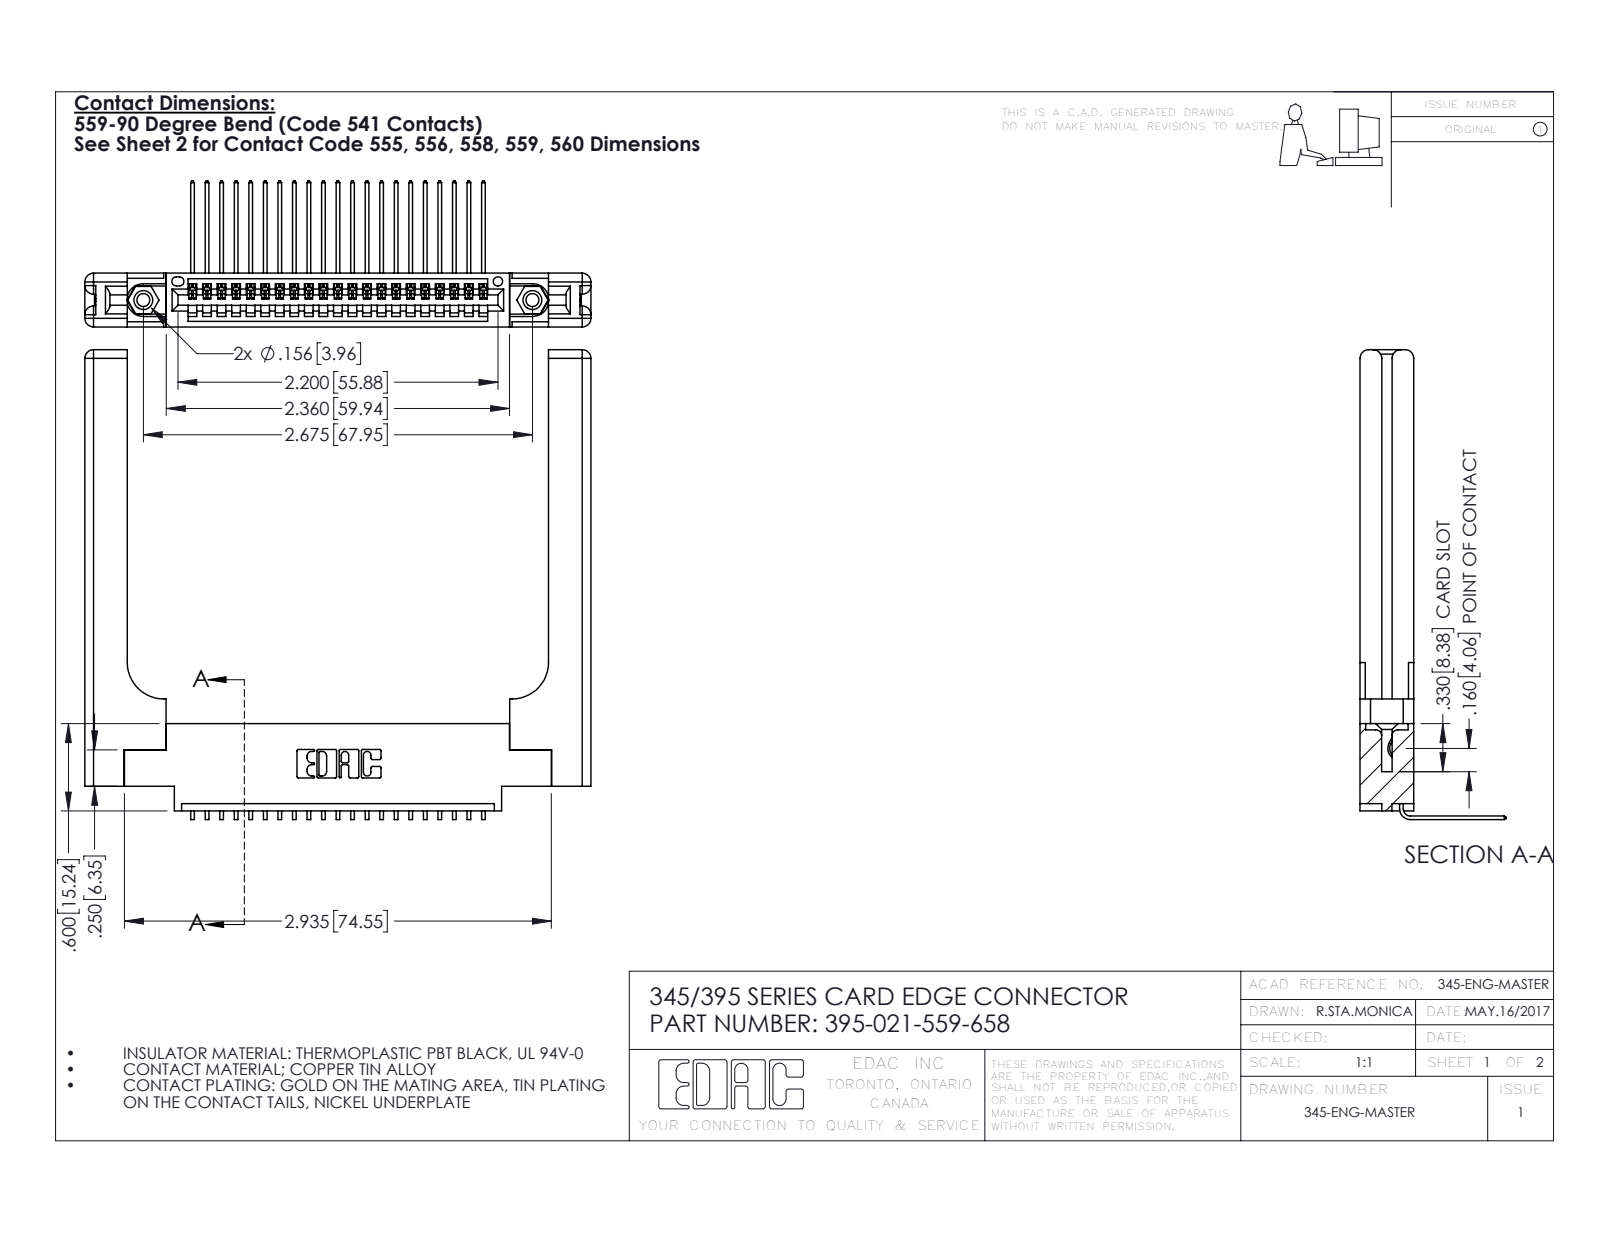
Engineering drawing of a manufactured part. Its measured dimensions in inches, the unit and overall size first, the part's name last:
Units: inches
Overall size (bounding box): 3.479 × 3.229 × 1.005
Round holes (diameter × count): ⌀0.089 ×2, ⌀0.125 ×2, ⌀0.156 ×2, ⌀0.064 ×1
Round bosses / shafts (diameter × count): ⌀0.155 ×2
Partial cylindrical surfaces — rounded edges, fillets, slot ends (radius × count): R0.006 ×42, R0.01 ×22, R0.06 ×16, R0.007 ×6, R0.031 ×6, R0.026 ×3, R0.03 ×2, R0.031 ×2
Main face-to-face distances: 0.37, 0.072, 0.298, 0.148, 0.15, 0.077, 0.22, 0.123, 0.098, 0.272
Hole centre spacings: 0.27, 2.441, 2.675
Volume: 1.018 in³ · Surface area: 25.46 in²
Bodies: 26 solids, 1646 faces (1114 planar, 472 cylindrical, 60 other)
Part name (STEP PRODUCT): 345-220-058_345-220-058; 345-292-001_558 559 Tail - 1; 395-021-559-658; 345-250-001_345-250-001-102 (+1 more)
STEP written by: SolidWorks 2016 (CONFIG_CONTROL_DESIGN)
